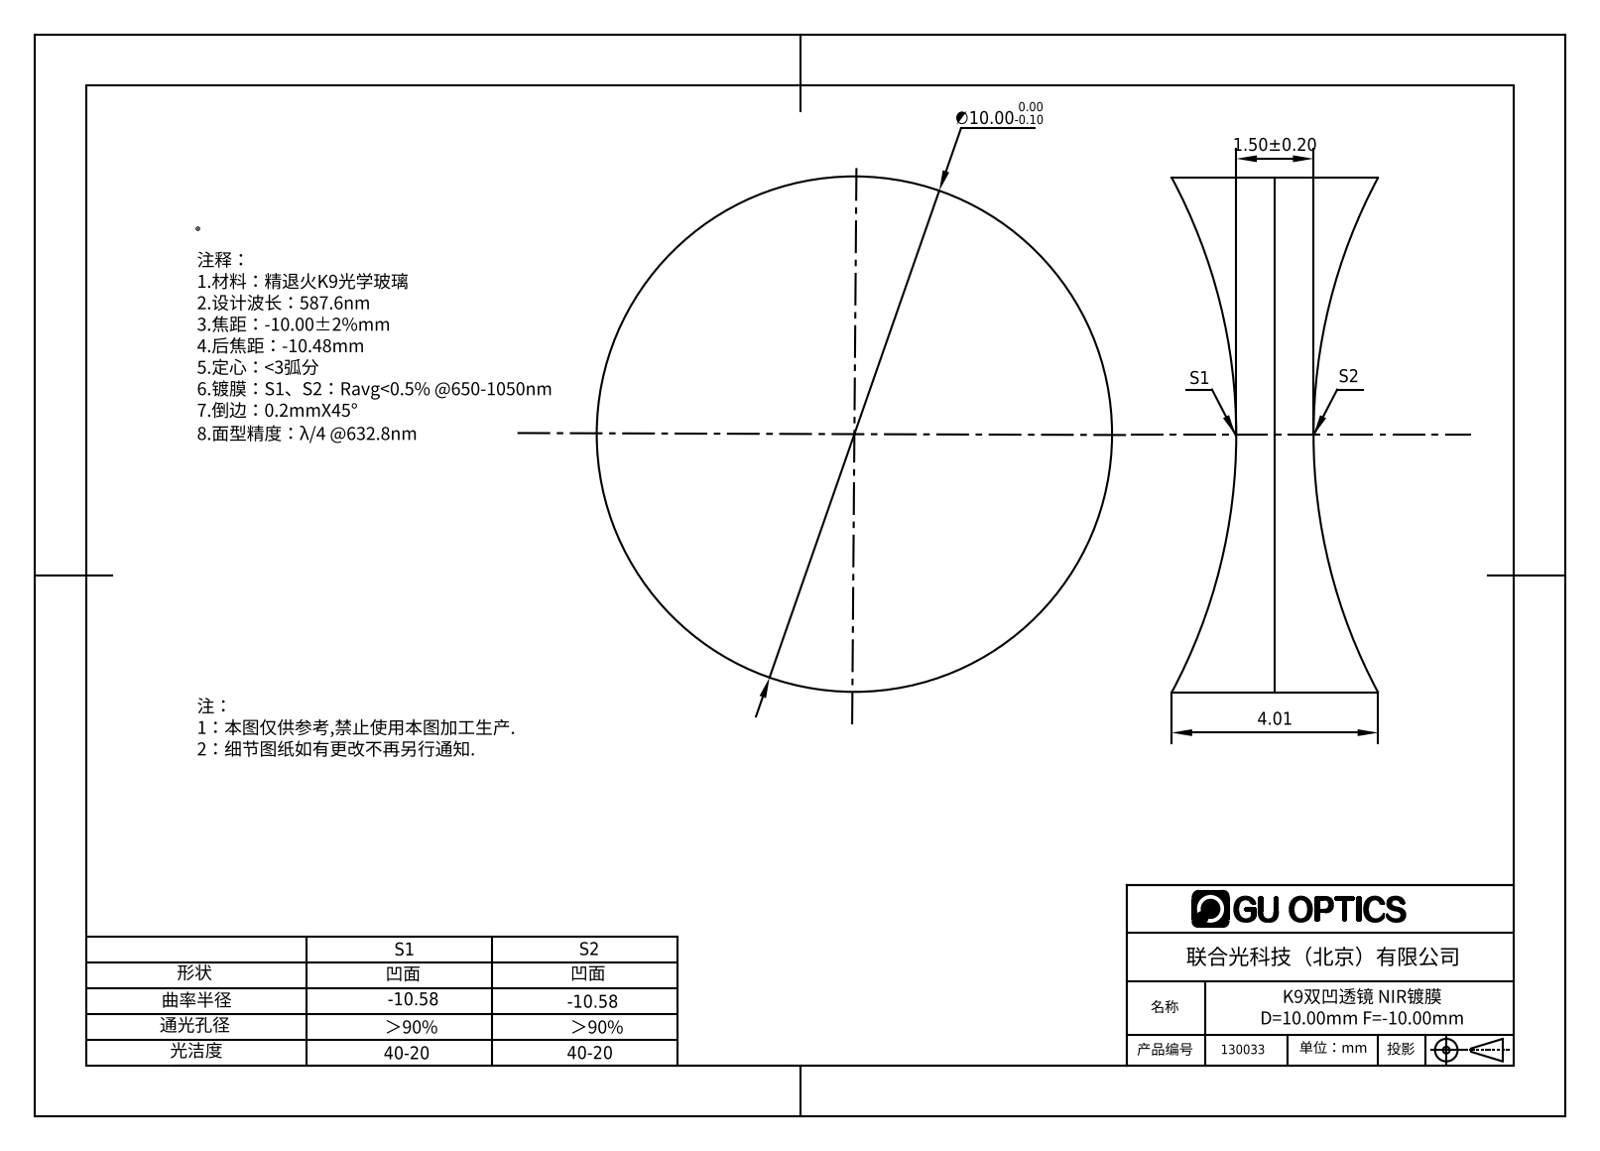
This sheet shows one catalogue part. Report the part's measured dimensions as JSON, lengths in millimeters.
{"part_name": "130007", "step_written_by": "SolidWorks 2016 (AUTOMOTIVE_DESIGN)", "units": "millimeters", "bodies": {"solids": 1, "faces": 6, "planar": 0, "cylindrical": 2, "other": 4}, "overall_size": [10, 10, 4.01], "volume_mm3": 214, "surface_area_mm2": 293, "round_bosses_or_shafts": [[10, 1]]}
